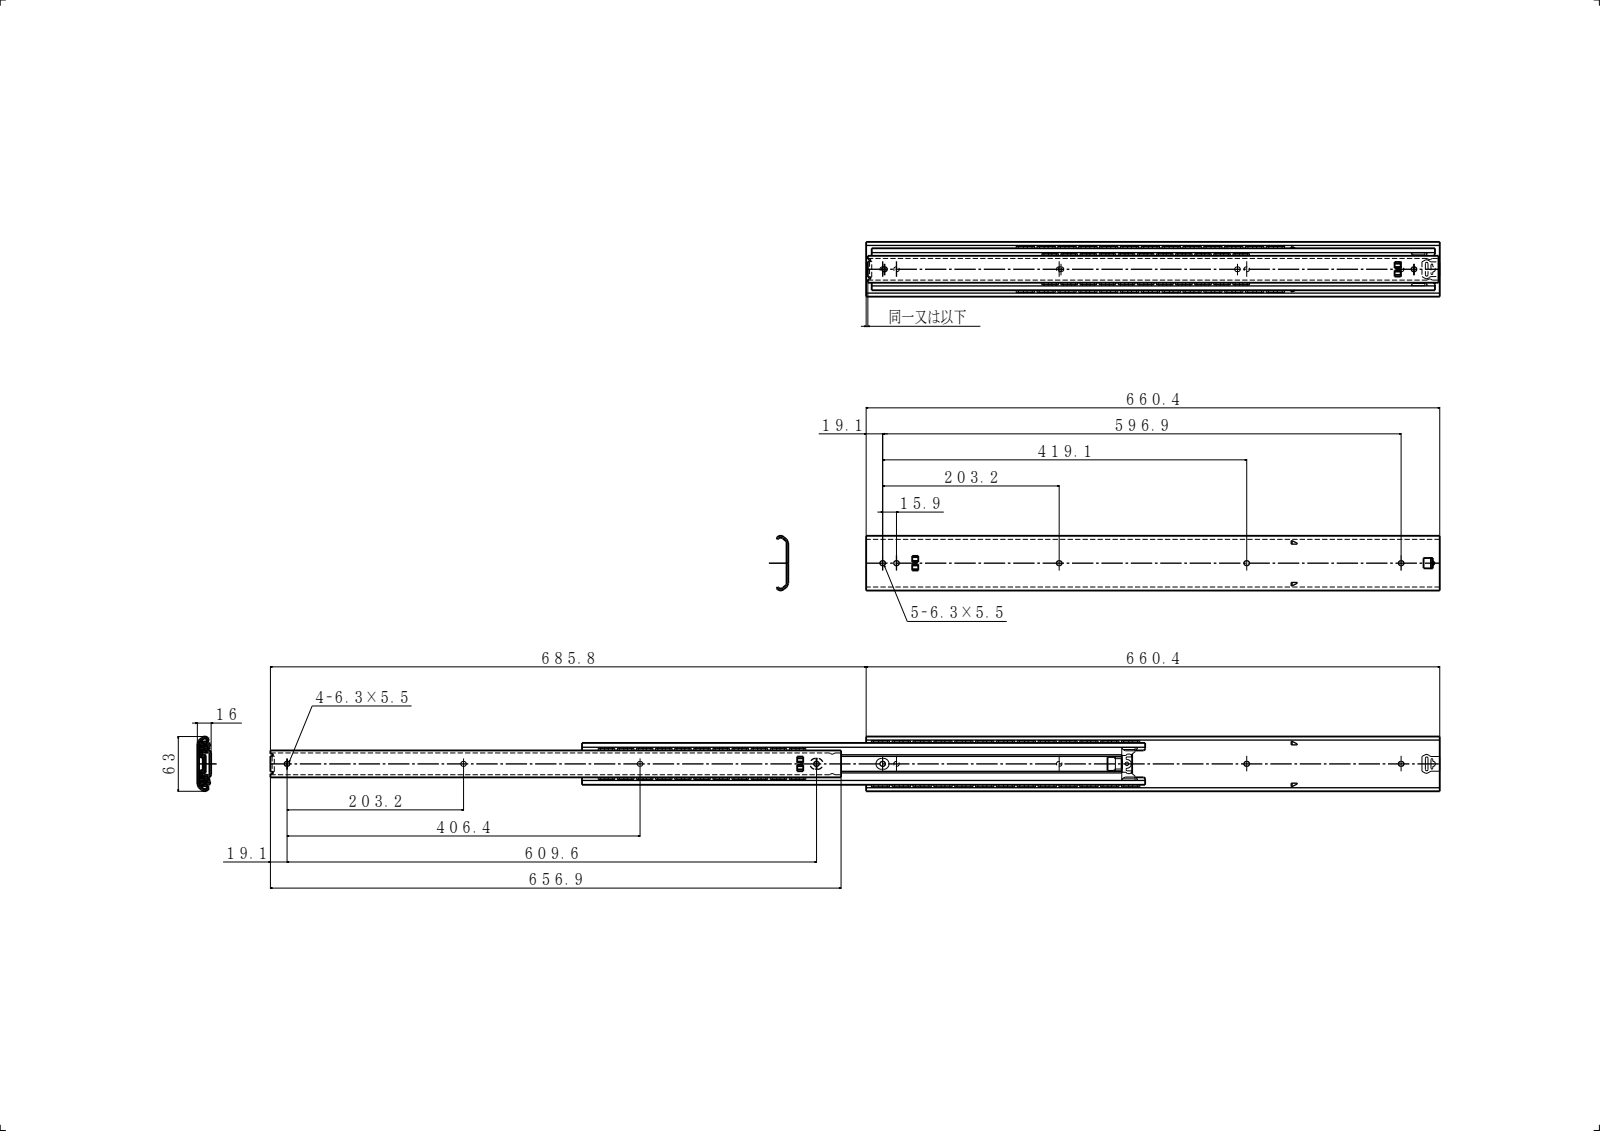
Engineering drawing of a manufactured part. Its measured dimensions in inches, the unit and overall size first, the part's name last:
Units: inches
Overall size (bounding box): 53.021 × 2.48 × 0.63
Round holes (diameter × count): ⌀0.213 ×1
Round bosses / shafts (diameter × count): ⌀0.197 ×1
Partial cylindrical surfaces — rounded edges, fillets, slot ends (radius × count): R0.039 ×22, R0.02 ×18, R0.108 ×18, R0.079 ×16, R0.012 ×12, R0.047 ×10, R0.008 ×8, R0.063 ×8
Main face-to-face distances: 0.079, 0.551, 0.061, 0.472, 0.63, 0.161, 0.051, 0.5, 0.113, 0.439
Volume: 16 in³ · Surface area: 461.7 in²
Bodies: 10 solids, 629 faces (389 planar, 238 cylindrical, 2 other)
Part name (STEP PRODUCT): C630-26; C630-26 IM; PN161A; PN68 (+5 more)
STEP written by: SolidWorks 2019 (CONFIG_CONTROL_DESIGN)
